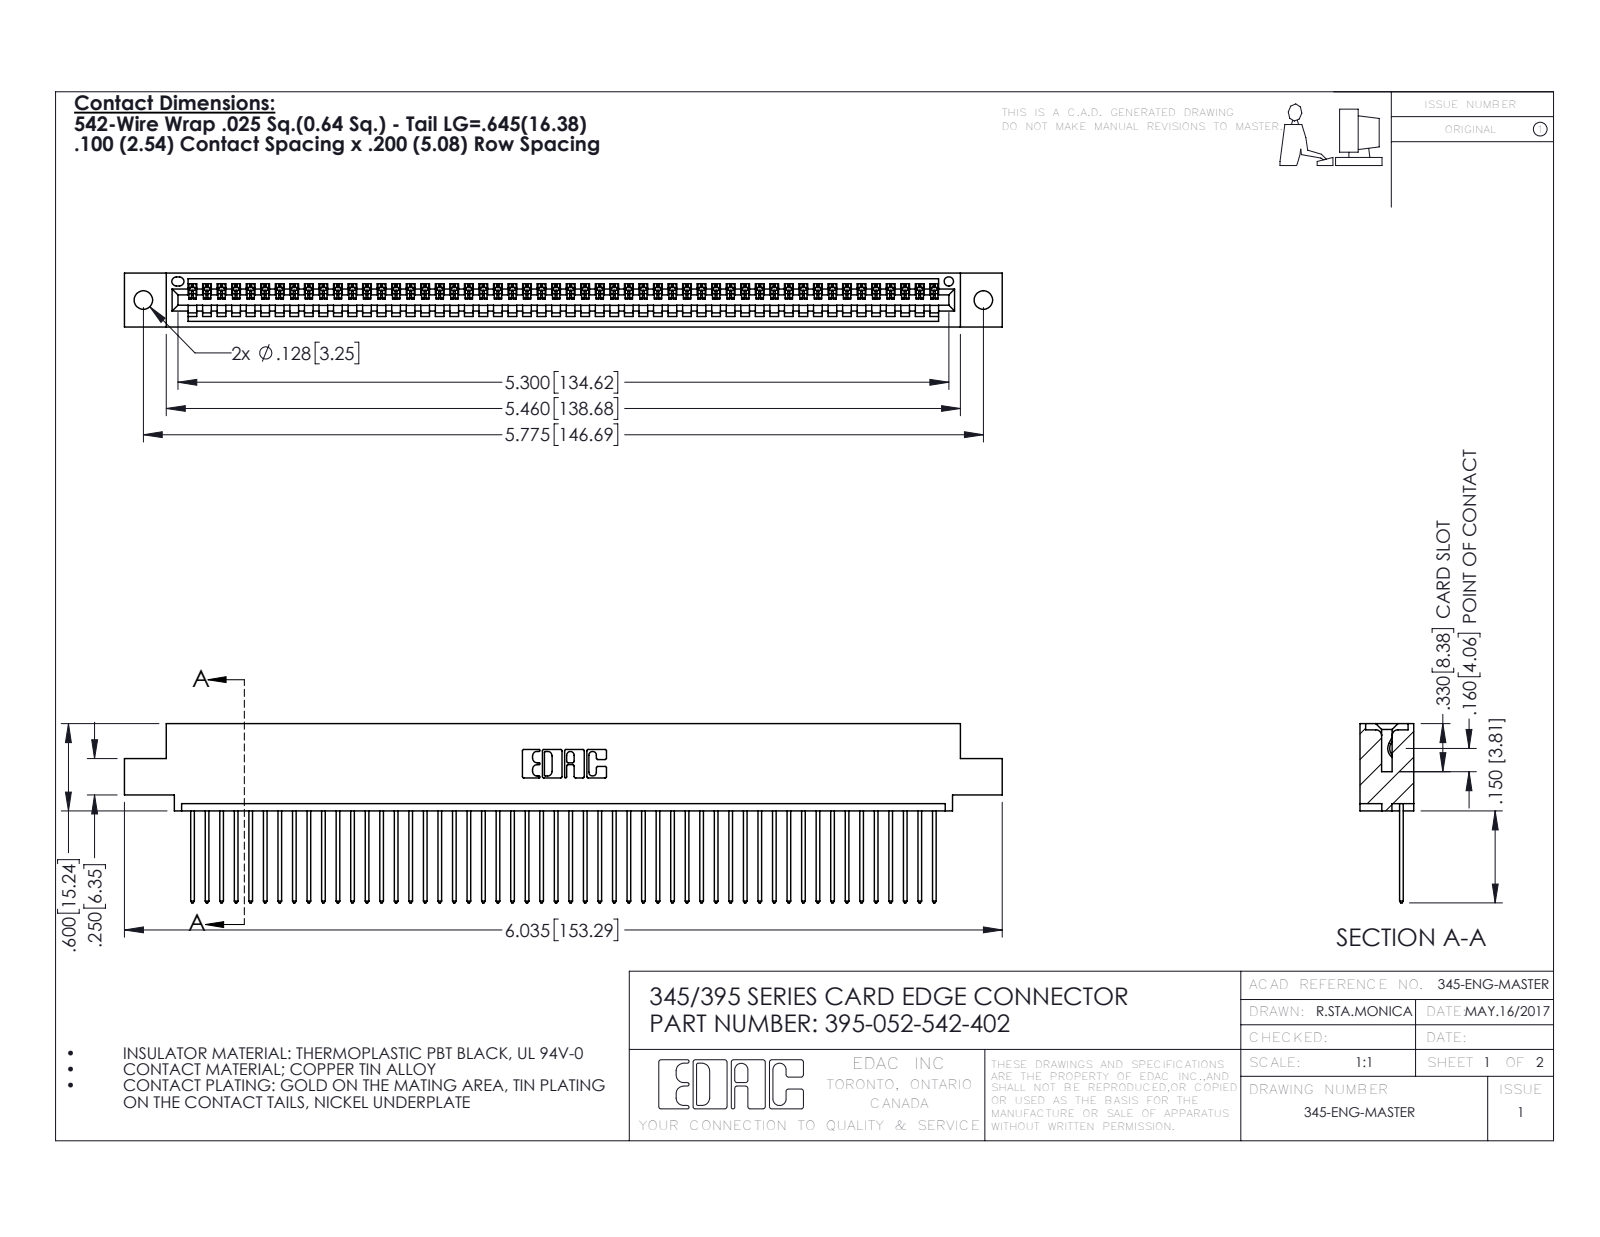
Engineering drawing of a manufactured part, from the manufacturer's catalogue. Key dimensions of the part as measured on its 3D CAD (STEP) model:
Part name (STEP PRODUCT): 395-052-542-402; 345-292-001_345-293-142; 345 Part_0.110 Offset - 0.128 Dia
STEP written by: SolidWorks 2016 (CONFIG_CONTROL_DESIGN)
Units: inches
Bodies: 53 solids, 3146 faces (2164 planar, 982 cylindrical, 0 other)
Overall size (bounding box): 6.035 × 1.232 × 0.37
Volume: 0.894 in³ · Surface area: 31.22 in²
Round holes (diameter × count): ⌀0.128 ×2, ⌀0.064 ×1
Partial cylindrical surfaces — rounded edges, fillets, slot ends (radius × count): R0.006 ×104, R0.01 ×104, R0.01 ×22, R0.007 ×6, R0.031 ×6, R0.026 ×3, R0.031 ×2, R0.04 ×2
Main face-to-face distances: 0.072, 0.298, 0.098, 0.272, 0.025, 0.37, 0.2, 0.225, 0.149, 0.072
Hole centre spacings: 0.27, 5.539, 5.775
